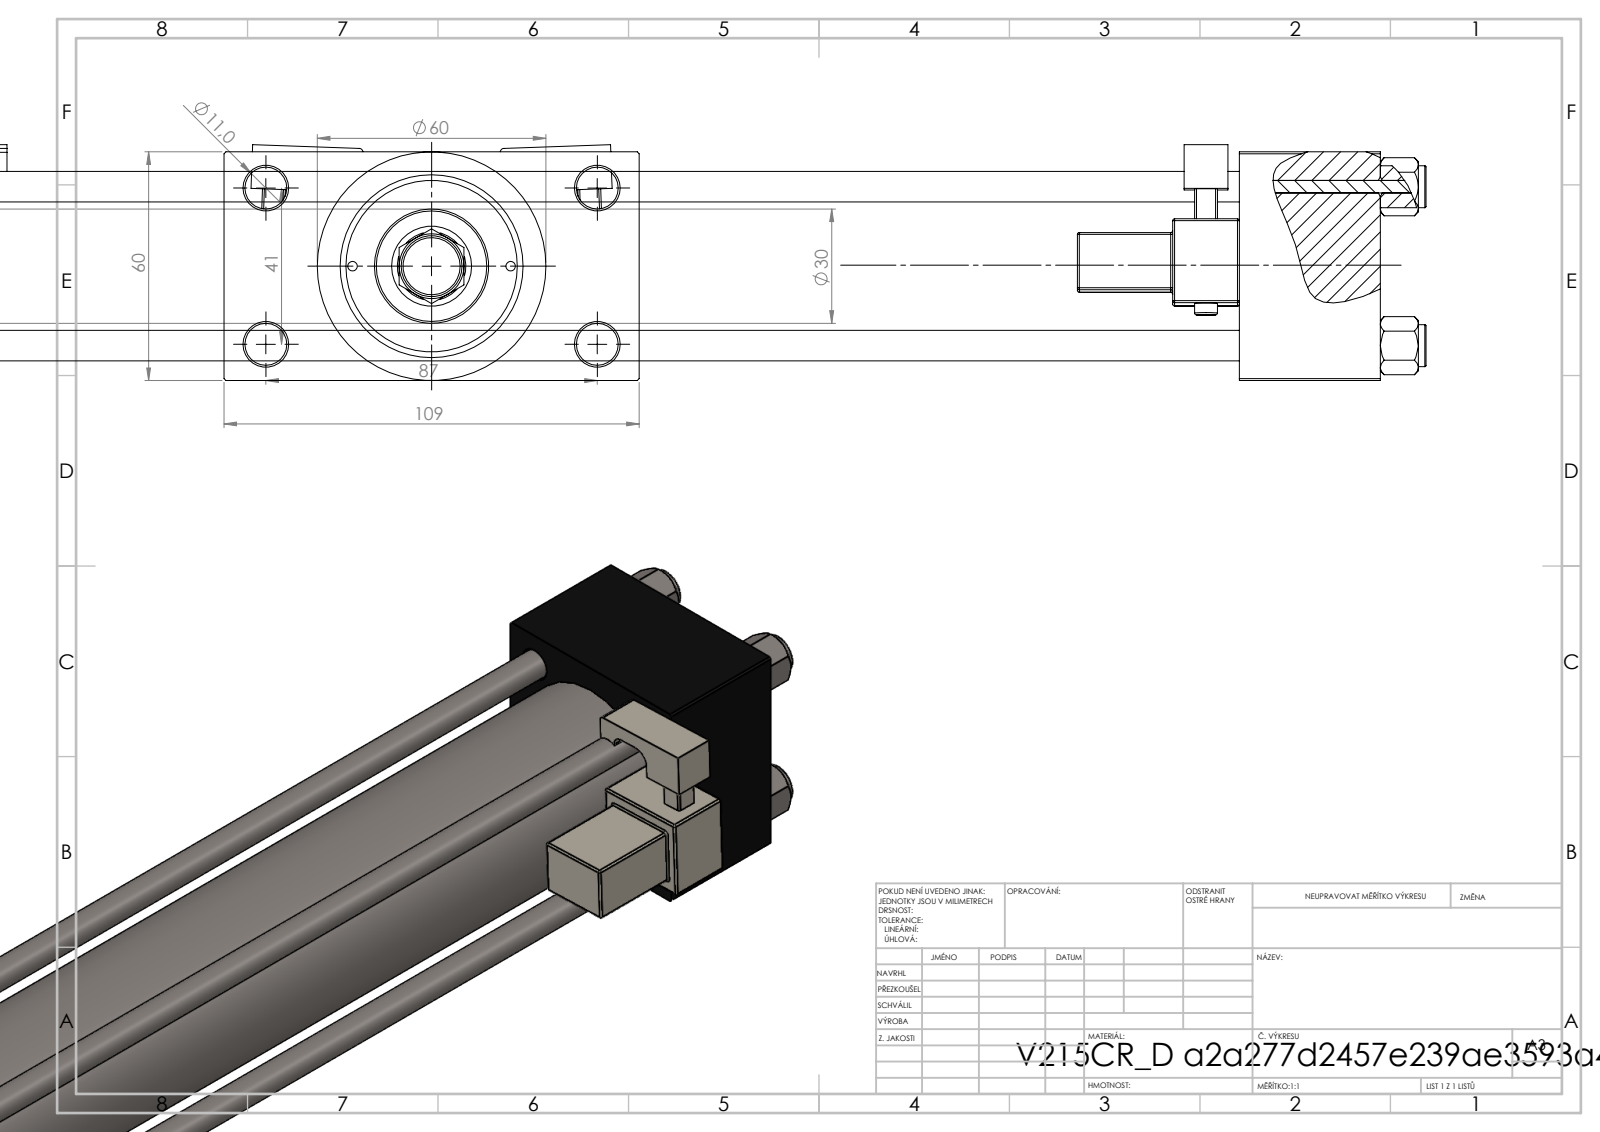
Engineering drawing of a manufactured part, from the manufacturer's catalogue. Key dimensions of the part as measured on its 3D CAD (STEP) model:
Part name (STEP PRODUCT): V215CR_D_TYCINKA; MFA; V215CR_D_Body; V215CR_MSU (+3 more)
STEP written by: SolidWorks 2019 (CONFIG_CONTROL_DESIGN)
Units: millimetres
Bodies: 14 solids, 1318 faces (574 planar, 156 cylindrical, 588 other)
Overall size (bounding box): 493 × 109 × 61.9
Volume: 799 596 mm³ · Surface area: 256 287 mm²
Round holes (diameter × count): ⌀8 ×4, ⌀11 ×4, ⌀2.5 ×2, ⌀7 ×2, ⌀16.66 ×2, ⌀24 ×2, ⌀8.5 ×1, ⌀18 ×1, ⌀21 ×1, ⌀31 ×1, ⌀40 ×1, ⌀45 ×1
Round bosses / shafts (diameter × count): ⌀11 ×4, ⌀6 ×2, ⌀60 ×1, ⌀46 ×1, ⌀30 ×1, ⌀16 ×1, ⌀10 ×1
Partial cylindrical surfaces — rounded edges, fillets, slot ends (radius × count): R0.5 ×48, R1 ×2, R2.5 ×2, R4 ×2, R8.5 ×1
Main face-to-face distances: 60, 338, 24.5, 84.5, 37, 375, 418, 381, 43, 109
Hole centre spacings: 20.85, 22.65, 29.49, 30.62, 41.7, 46.53, 47.15, 48.09
